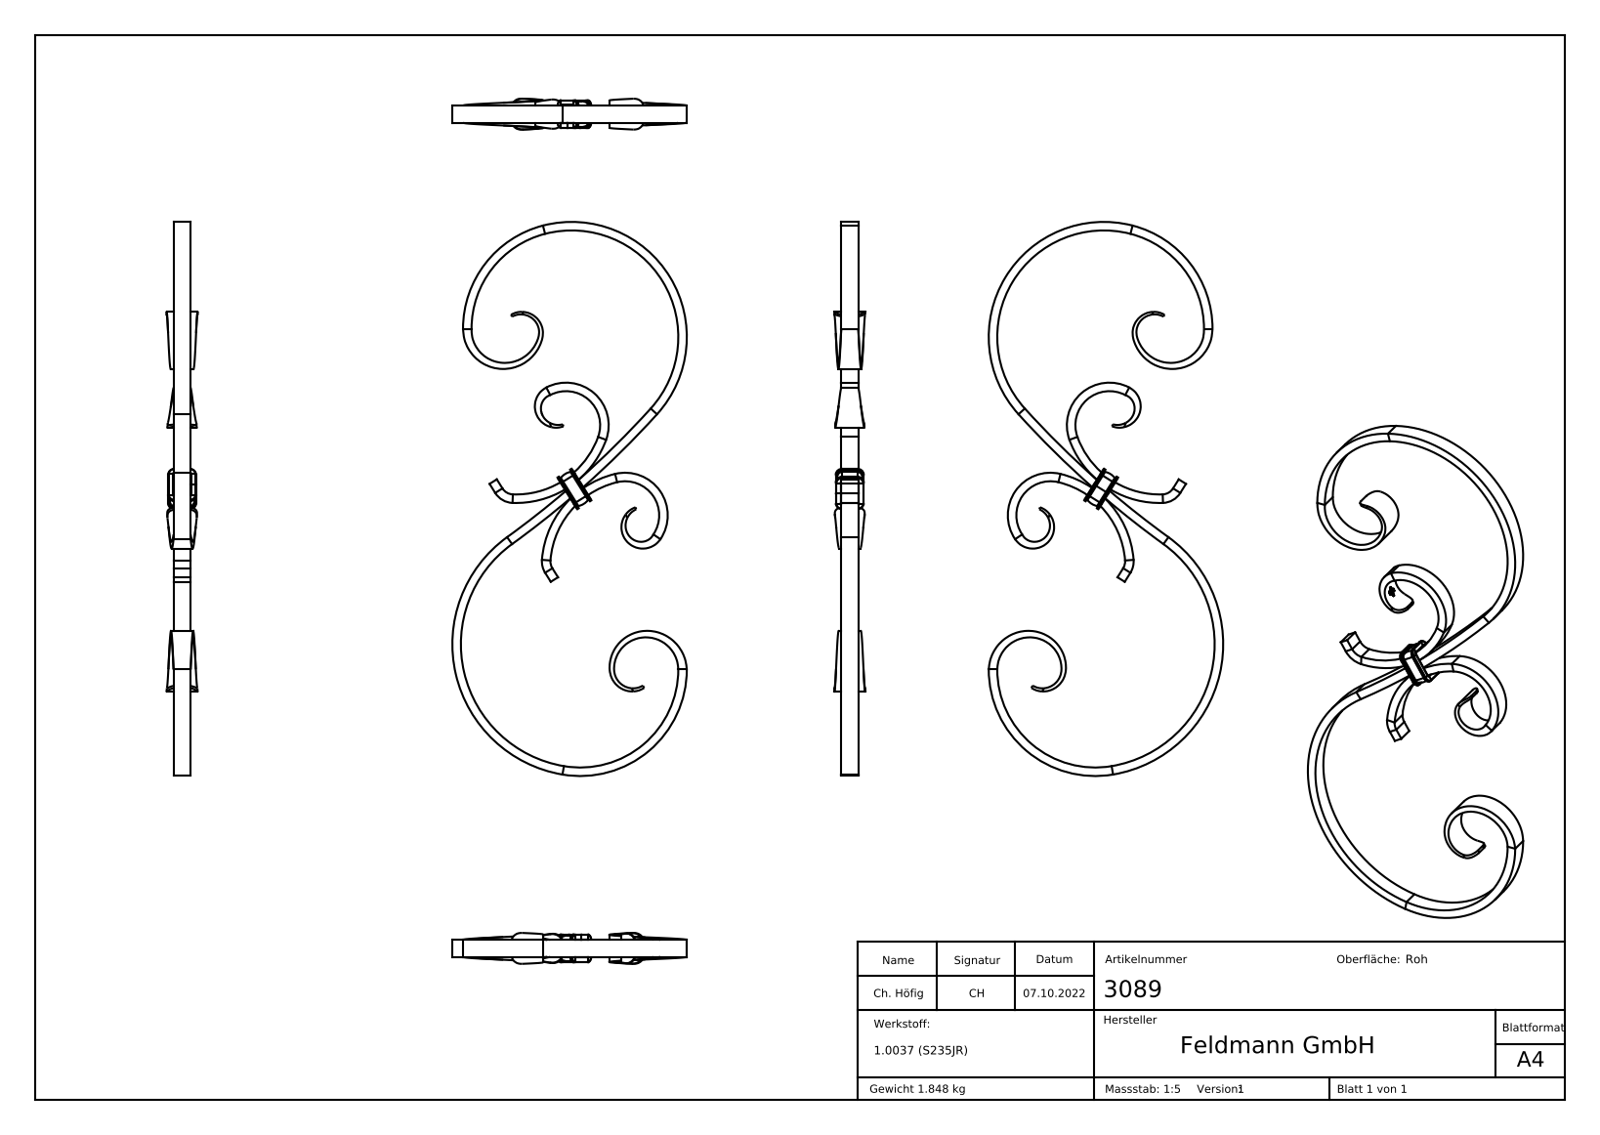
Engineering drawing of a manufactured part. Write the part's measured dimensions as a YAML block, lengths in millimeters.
part_name: "3089"
step_written_by: "SolidWorks 2018 (CONFIG_CONTROL_DESIGN)"
units: millimeters
bodies: {solids: 2, faces: 447, planar: 169, cylindrical: 81, other: 197}
overall_size: [520, 220, 29.05]
volume: 236929
surface_area: 96648
partial_cylinders:
  - {radius: 0.5, count: 31}
  - {radius: 1.1, count: 4}
  - {radius: 6.1, count: 4}
  - {radius: 15.12, count: 4}
  - {radius: 100, count: 3}
  - {radius: 12, count: 2}
  - {radius: 20, count: 2}
  - {radius: 32, count: 2}
face_to_face_distances: [16, 16.1, 16.2, 8, 2, 14, 57, 73, 49, 65]
